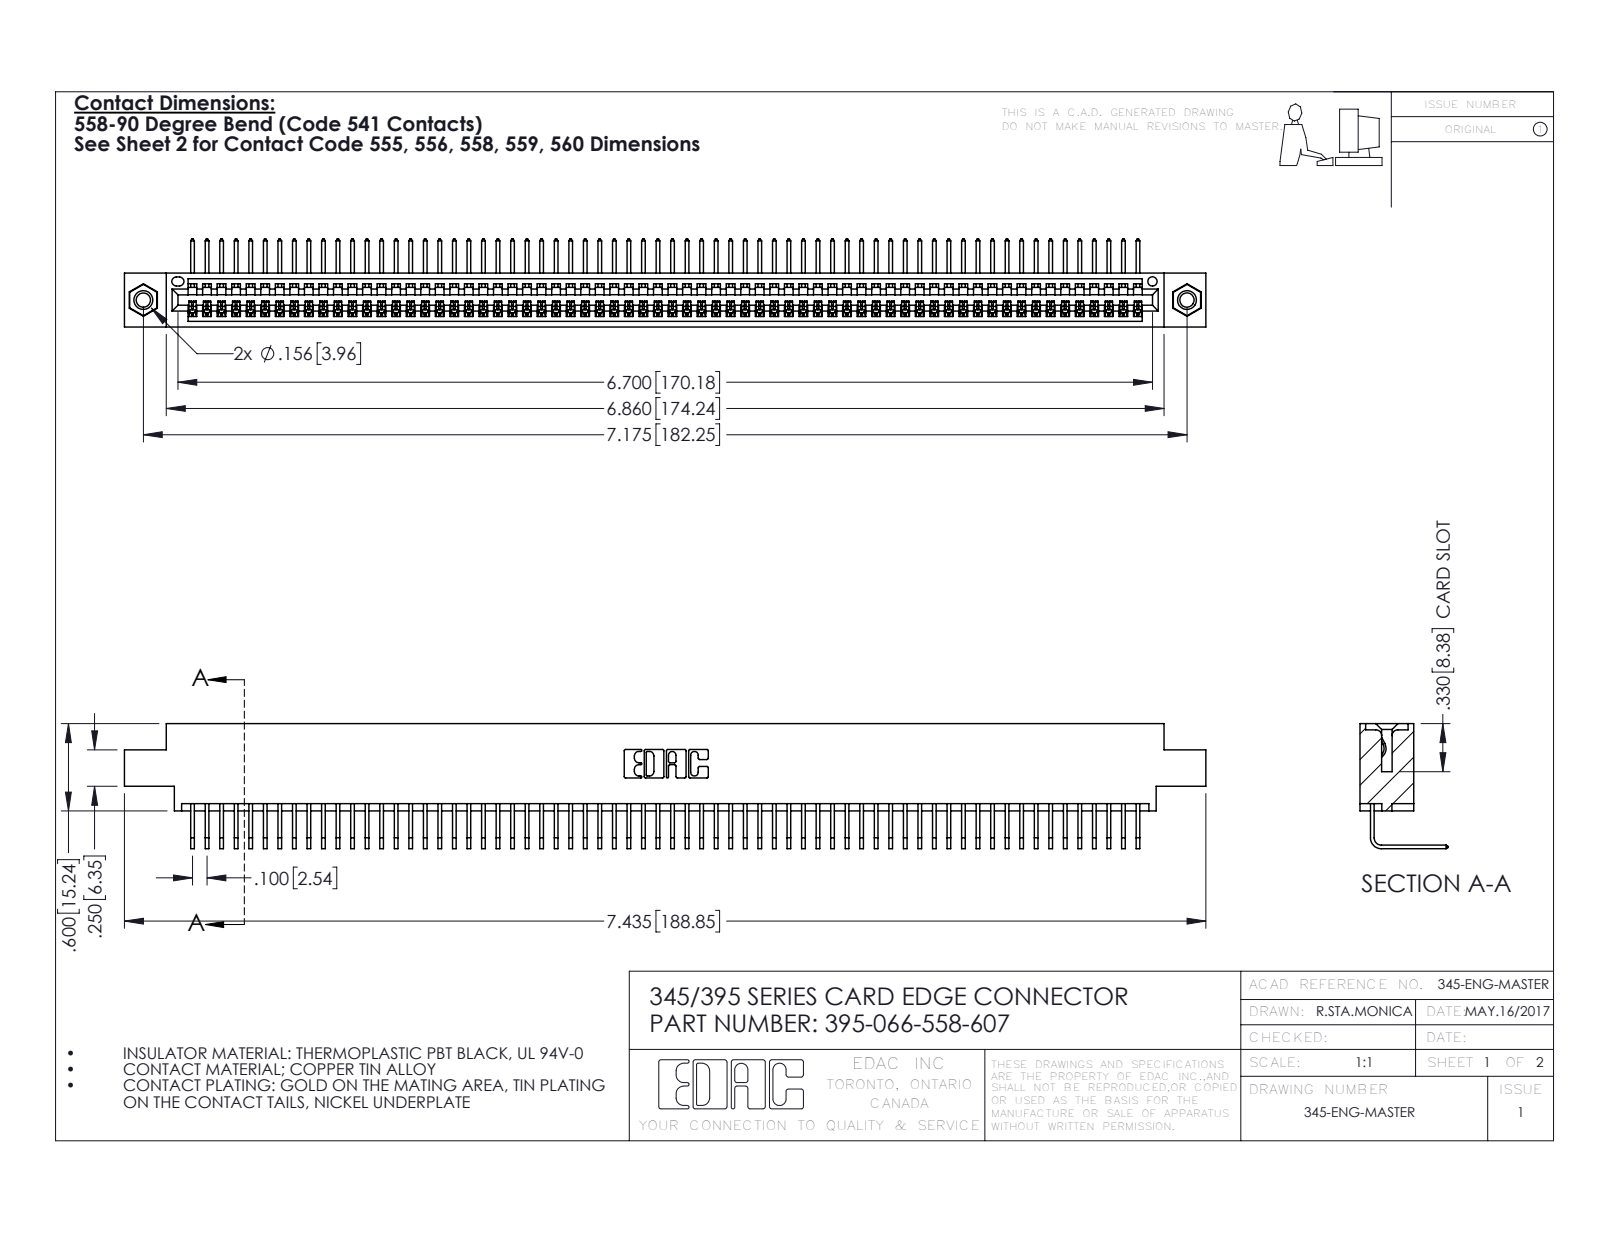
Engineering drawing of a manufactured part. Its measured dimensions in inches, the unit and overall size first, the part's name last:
Units: inches
Overall size (bounding box): 7.435 × 0.859 × 0.605
Round holes (diameter × count): ⌀0.098 ×2, ⌀0.125 ×2, ⌀0.156 ×2, ⌀0.064 ×1
Round bosses / shafts (diameter × count): ⌀0.155 ×2
Partial cylindrical surfaces — rounded edges, fillets, slot ends (radius × count): R0.006 ×132, R0.01 ×22, R0.007 ×6, R0.031 ×6, R0.026 ×3, R0.031 ×2, R0.04 ×2, R0.014 ×1
Main face-to-face distances: 0.072, 0.298, 0.37, 0.2, 0.098, 0.272, 0.025, 0.225, 0.175, 0.149
Hole centre spacings: 0.27, 6.939, 7.175
Volume: 1.112 in³ · Surface area: 40.3 in²
Bodies: 69 solids, 4150 faces (2888 planar, 1246 cylindrical, 16 other)
Part name (STEP PRODUCT): 395-066-558-607; 345-250-001_345-250-005-103; 345-292-001_558 Tail - 2; 345 Part_0.170 Offset - 0.156 Dia-TI
STEP written by: SolidWorks 2016 (CONFIG_CONTROL_DESIGN)
